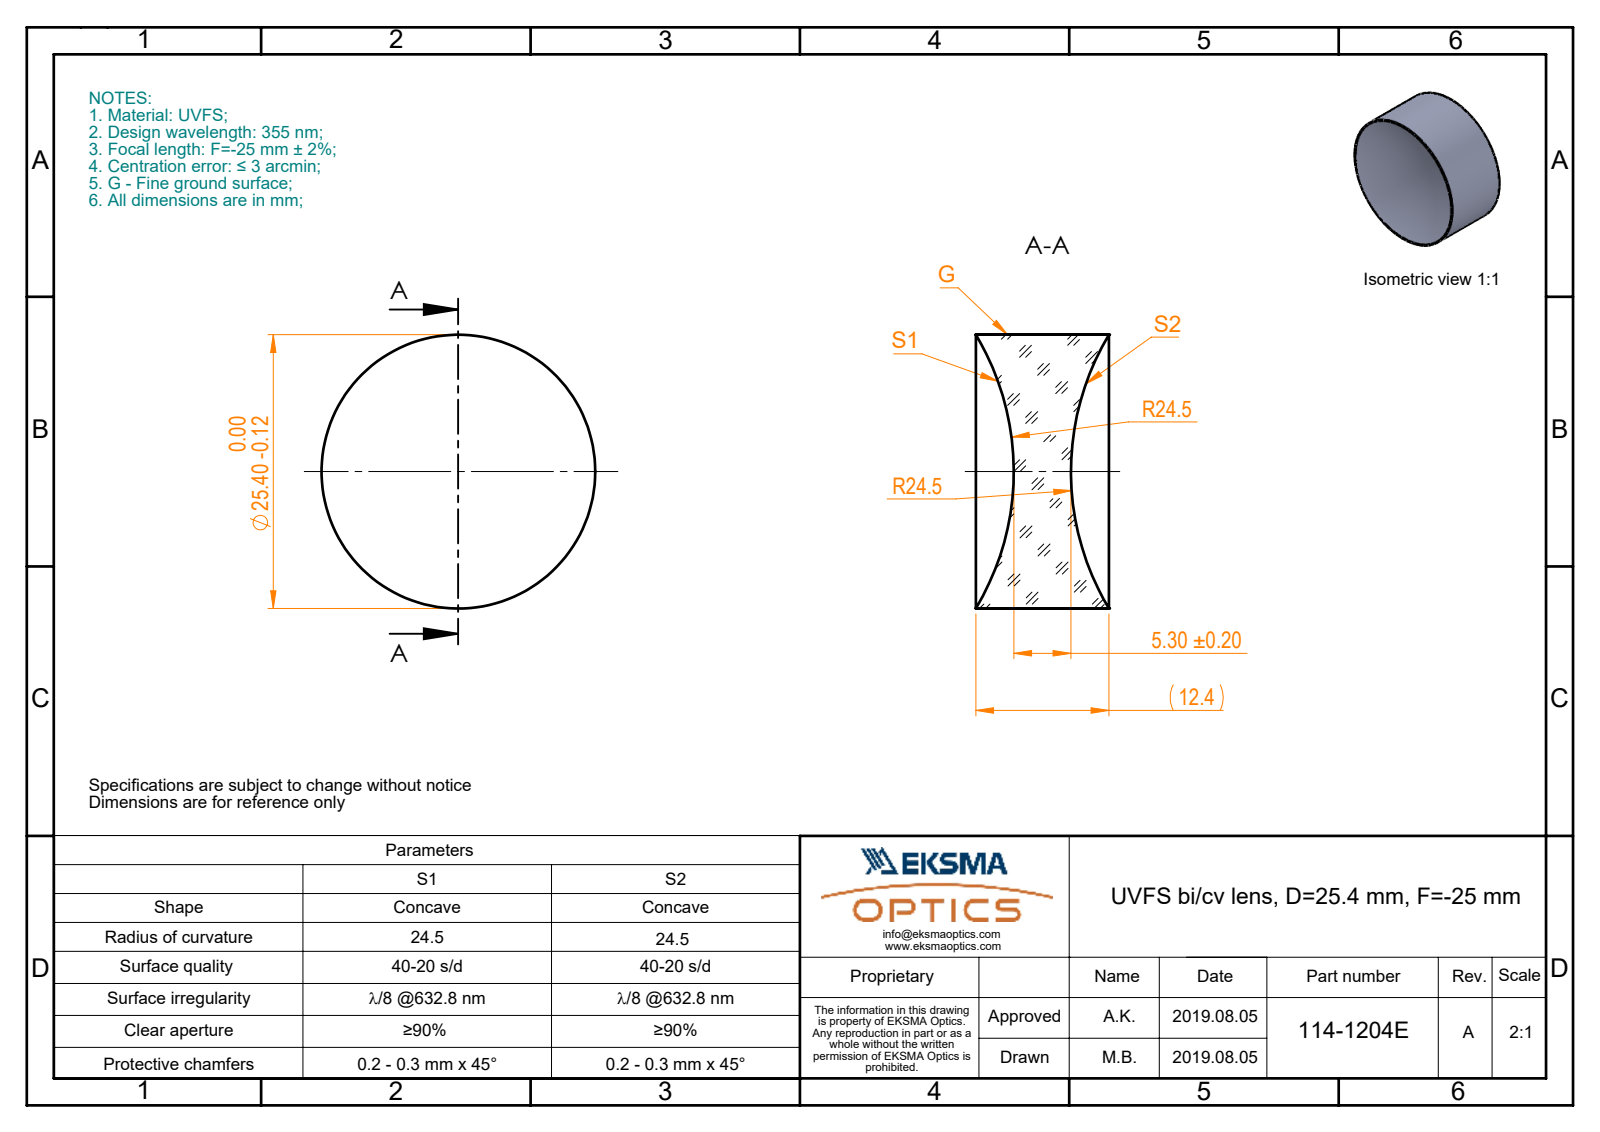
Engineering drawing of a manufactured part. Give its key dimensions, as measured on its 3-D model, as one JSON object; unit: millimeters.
{"part_name": "114-1204E.zmx; surfaces 1,2", "step_written_by": "Spatial InterOp 3D (AUTOMOTIVE_DESIGN)", "units": "millimeters", "bodies": {"solids": 1, "faces": 5, "planar": 2, "cylindrical": 1, "other": 2}, "overall_size": [25.4, 25.4, 9.06], "volume_mm3": 3249, "surface_area_mm2": 1795, "round_bosses_or_shafts": [[25.4, 1]], "face_to_face_distances": [9.06]}
